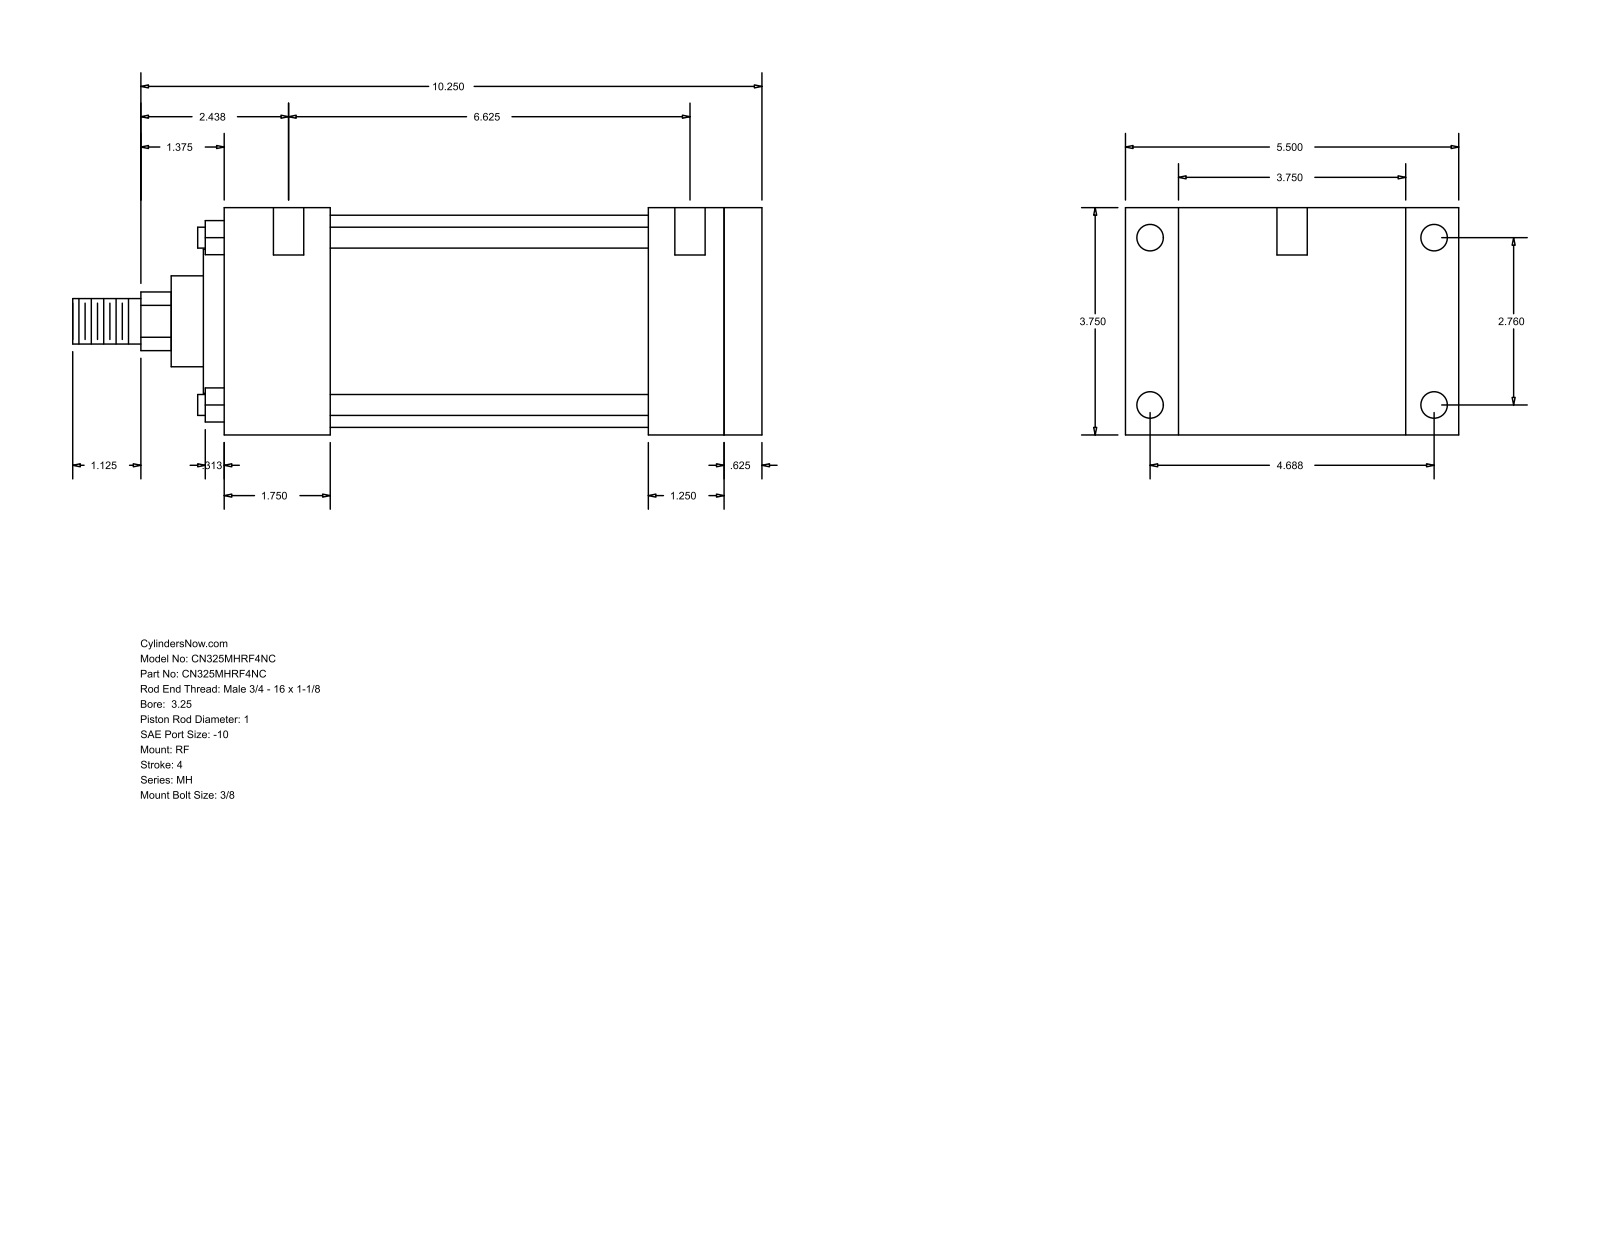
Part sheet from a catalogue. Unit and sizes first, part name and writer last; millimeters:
Units: millimetres
Overall size (bounding box): 288.93 × 139.7 × 95.25
Round holes (diameter × count): ⌀5.56 ×4, ⌀11.13 ×4, ⌀12.7 ×2
Round bosses / shafts (diameter × count): ⌀8.76 ×4, ⌀88.9 ×1, ⌀60.33 ×1, ⌀38.1 ×1, ⌀25.4 ×1, ⌀19.05 ×1
Partial cylindrical surfaces — rounded edges, fillets, slot ends (radius × count): R12.29 ×1
Main face-to-face distances: 95.24, 225.43, 209.55, 15.88, 22.23, 117.47, 44.46, 165.09, 180.97, 177.8
Hole centre spacings: 70.1, 119.06, 138.16, 174.62, 1.58, 4.76, 168.28, 169.86
Bodies: 0 solids, 94 faces (65 planar, 29 cylindrical, 0 other)
Part name (STEP PRODUCT): MH_RF__0325_1
STEP written by: GSSL Pune (CONFIG_CONTROL_DESIGN)
